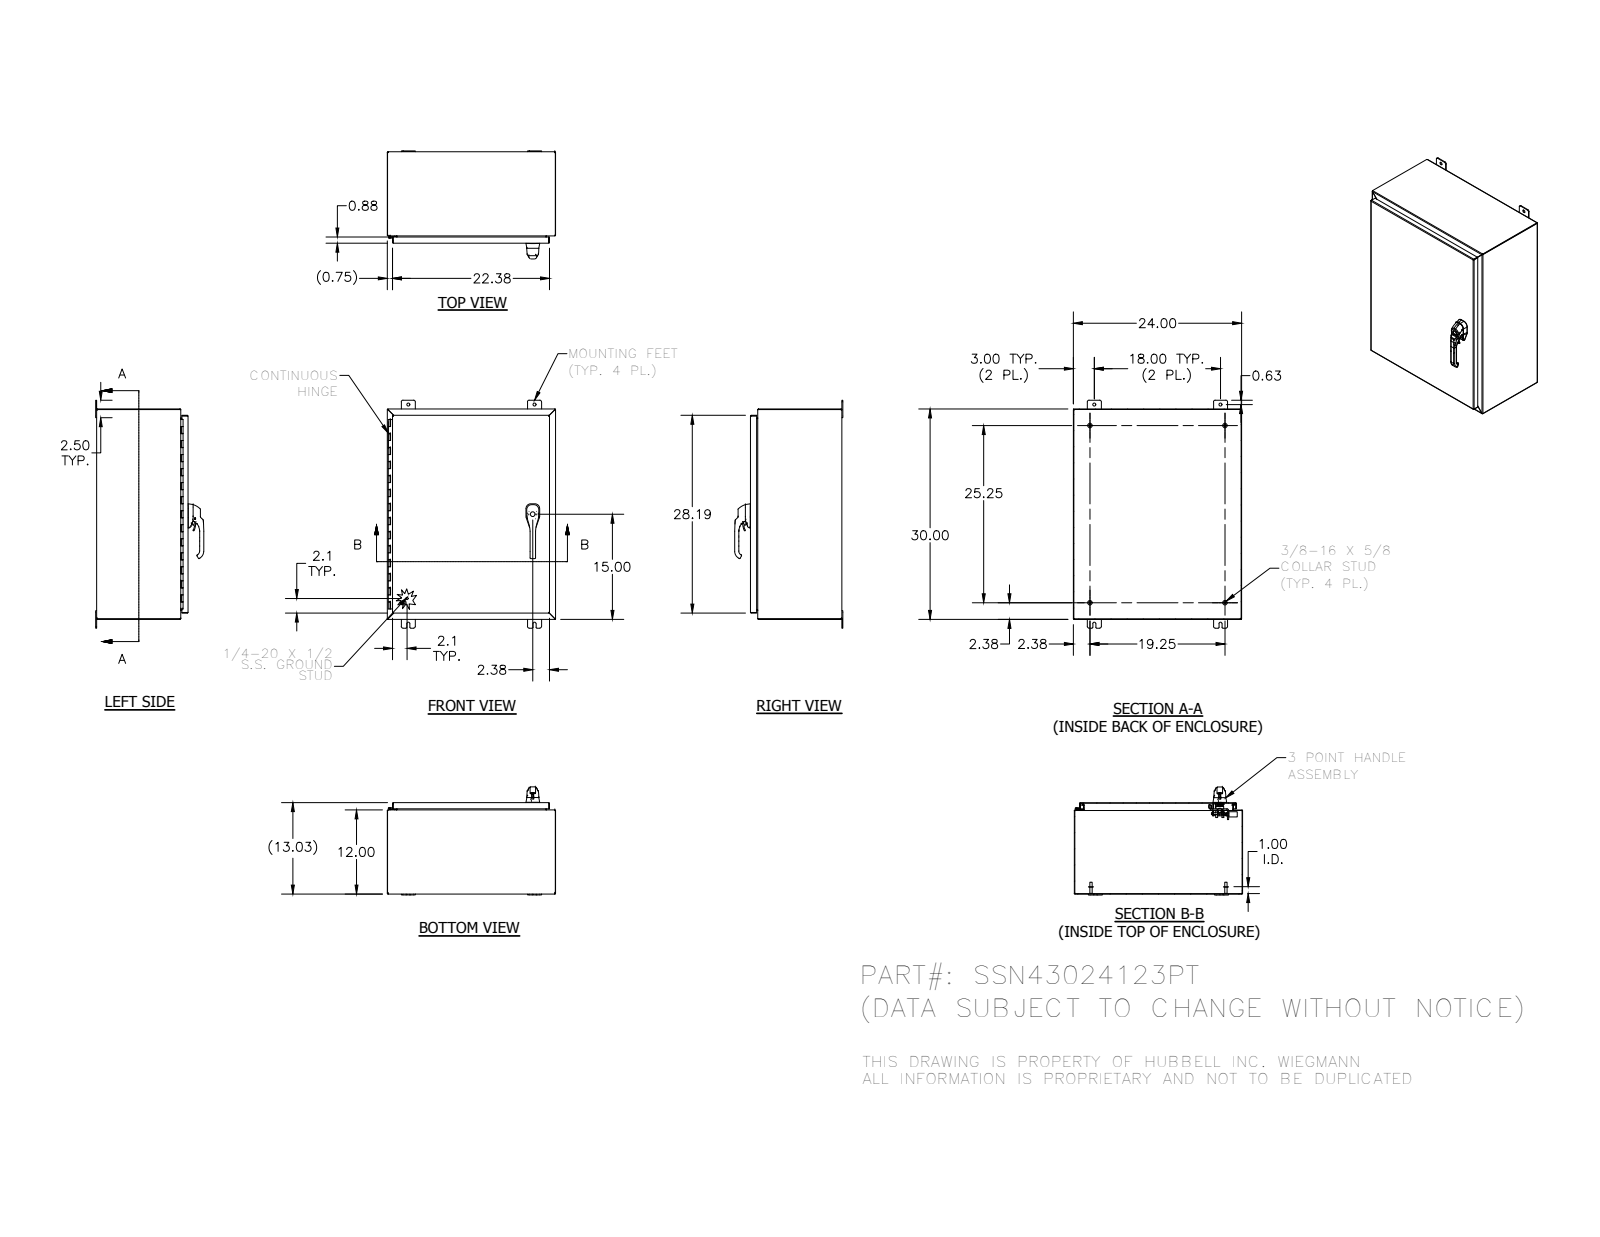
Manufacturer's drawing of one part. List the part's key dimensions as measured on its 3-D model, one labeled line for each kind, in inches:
Part name (STEP PRODUCT): 30254; HFW369101; 1091-B11_ASM; 328139T (+8 more)
STEP written by: SolidWorks 2014 (AUTOMOTIVE_DESIGN)
Units: inches
Bodies: 56 solids, 3128 faces (1047 planar, 1296 cylindrical, 785 other)
Overall size (bounding box): 32.5 × 24 × 15.408
Volume: 249.1 in³ · Surface area: 6 478 in²
Round holes (diameter × count): ⌀0.262 ×8, ⌀0.187 ×4, ⌀0.438 ×4, ⌀0.213 ×3, ⌀0.281 ×3, ⌀0.241 ×2, ⌀0.25 ×2, ⌀0.252 ×2, ⌀0.315 ×2, ⌀0.4 ×2, ⌀0.402 ×2, ⌀0.413 ×2
Round bosses / shafts (diameter × count): ⌀0.625 ×4, ⌀0.33 ×4, ⌀0.236 ×3, ⌀1 ×2, ⌀0.563 ×2, ⌀0.533 ×2, ⌀0.531 ×2, ⌀0.5 ×2
Partial cylindrical surfaces — rounded edges, fillets, slot ends (radius × count): R0.02 ×172, R0.012 ×113, R0.125 ×26, R0.031 ×24, R0.019 ×21, R0.105 ×20, R0.25 ×20, R0.025 ×16
Main face-to-face distances: 0.074, 12.959, 23.926, 12.885, 13.033, 29.926, 23.852, 24, 29.852, 30
Hole centre spacings: 0.38, 0.492, 0.76, 0.886, 20.428, 0.234, 0.258, 0.38
